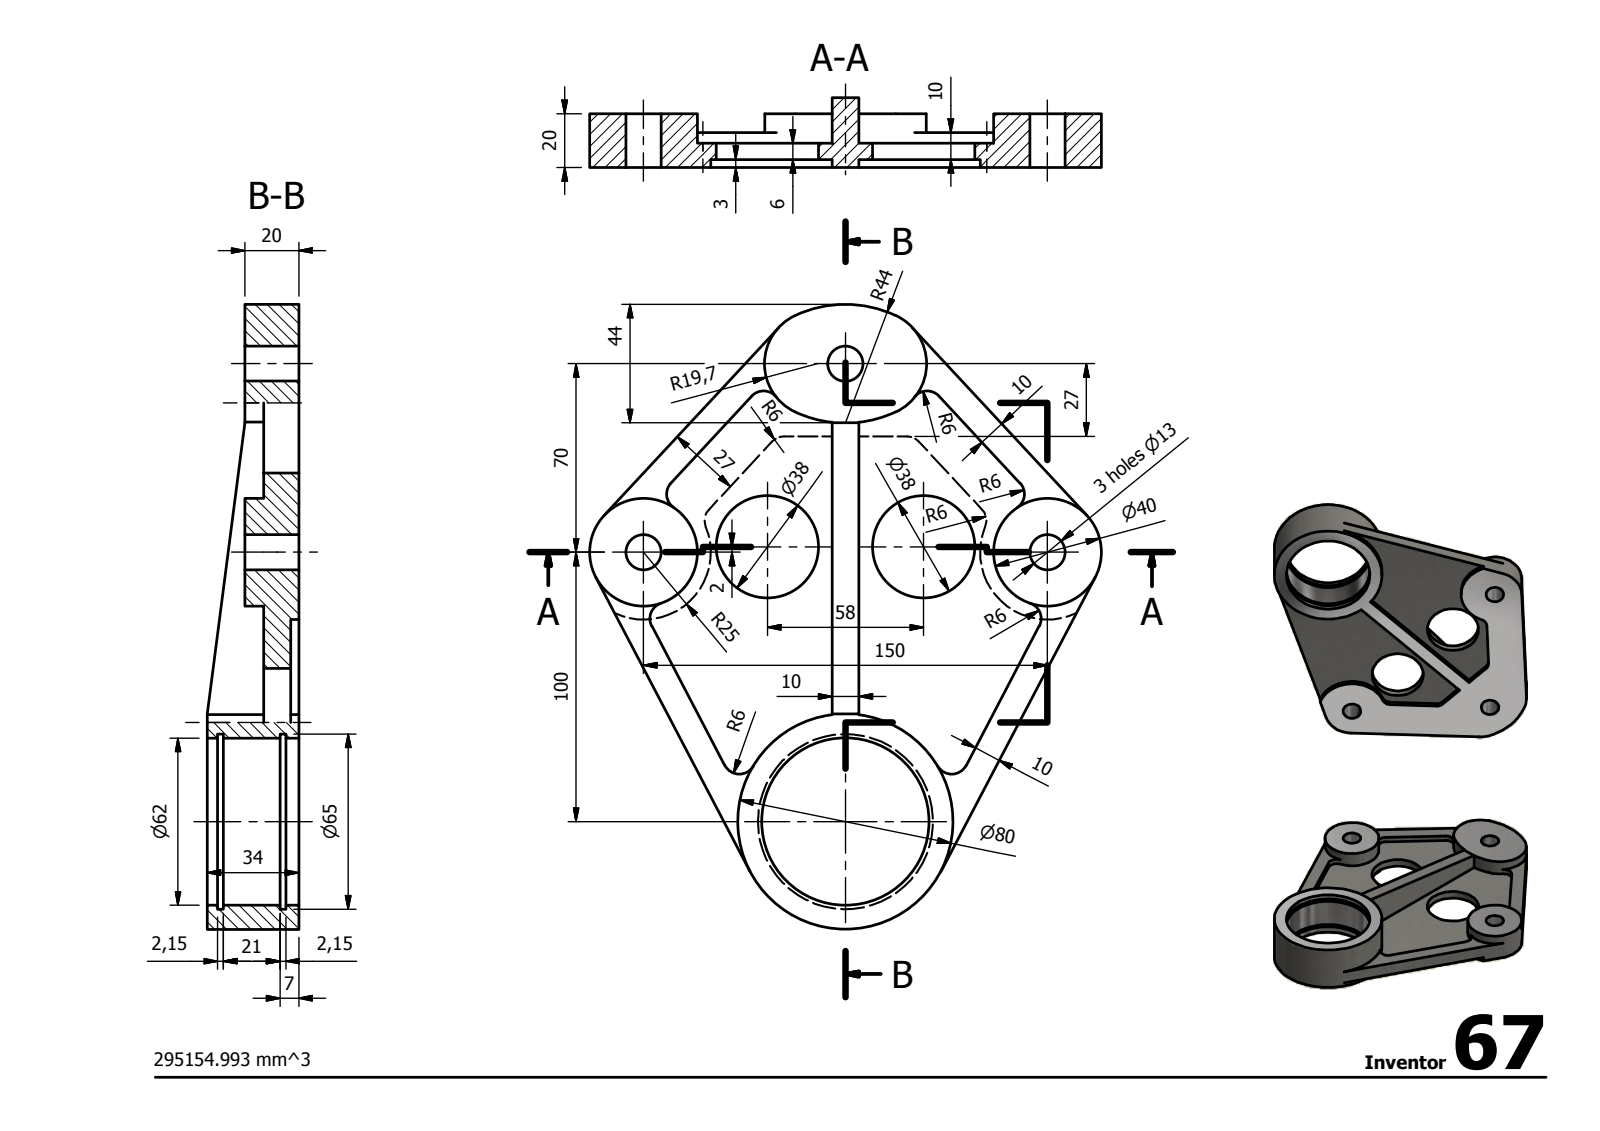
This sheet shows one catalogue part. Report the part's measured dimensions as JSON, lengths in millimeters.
{"step_written_by": "Autodesk Inventor 2014 (AUTOMOTIVE_DESIGN)", "units": "millimeters", "bodies": {"solids": 1, "faces": 66, "planar": 34, "cylindrical": 32, "other": 0}, "overall_size": [232, 190, 34], "volume_mm3": 295158, "surface_area_mm2": 78875, "round_holes": [[13, 3], [38, 2], [62, 1], [65, 1]], "round_bosses_or_shafts": [[40, 2], [80, 1]], "partial_cylinders_radius": [[6, 12], [19.7, 2], [25, 2], [44, 2]], "face_to_face_distances": [9, 6, 3, 10, 17, 20, 11, 7, 13, 4], "hole_center_spacings": [46.04, 73.93, 102.59, 104.02, 106.04, 125, 58, 150]}
